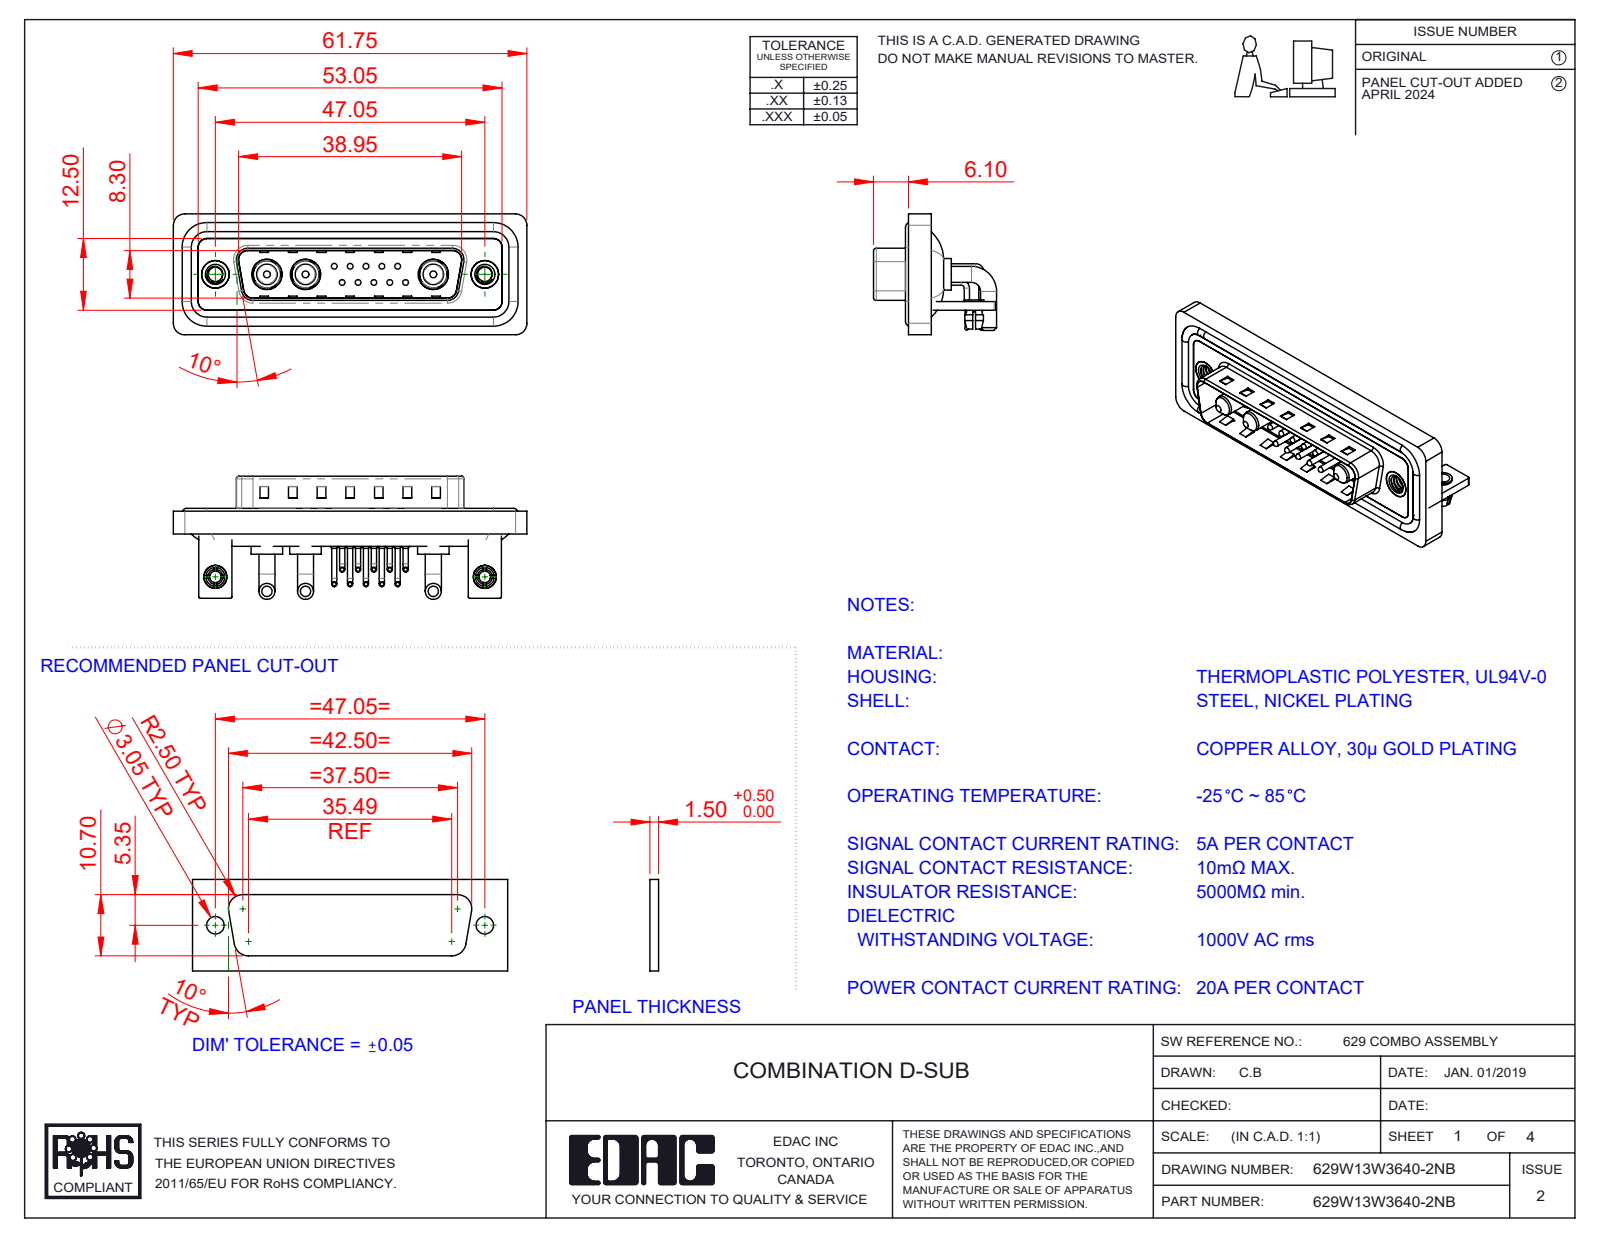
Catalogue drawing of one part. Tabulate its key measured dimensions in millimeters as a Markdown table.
| quantity | value |
| --- | --- |
| part name | 629Combo Waterproof Housing_25 Contacts; 629Combo Shell Front_25 Contacts; 629Combo Board Lock; 629Combo Stabilizer Bracket (+7 more) |
| STEP written by | SolidWorks 2023 (CONFIG_CONTROL_DESIGN) |
| units | millimeters |
| bodies | 27 solids, 1842 faces (947 planar, 661 cylindrical, 234 other) |
| overall size | 61.75 × 21.5 × 21.1 |
| volume | 7 918 mm³ |
| surface area | 13 295 mm² |
| round holes (diameter × count) | 2 × 12, 0.75 × 10, 1.6 × 10, 2.5 × 4, 4.85 × 3, 5.3 × 3, 3.2 × 2, 4 × 2, 4.8 × 2, 5 × 2 |
| round bosses / shafts (diameter × count) | 0.9 × 20, 1.5 × 10, 1 × 10, 0.65 × 10, 2.8 × 6, 1.6 × 4, 5.5 × 3, 5.2 × 3 |
| partial cylindrical surfaces (radius × count) | 2 × 19, 1.5 × 18, 0.25 × 16, 1.01 × 10, 0.5 × 9, 1.6 × 8, 0.6 × 4, 0.65 × 4 |
| main face-to-face distances | 0.4, 1.5, 0.8, 2.9, 2.1, 1.1, 4.1, 1.6, 3.7, 4.5 |
| hole center spacings | 3.16, 2.77, 5.04, 5.54, 7.49, 5.03, 8.31, 10.11 |
